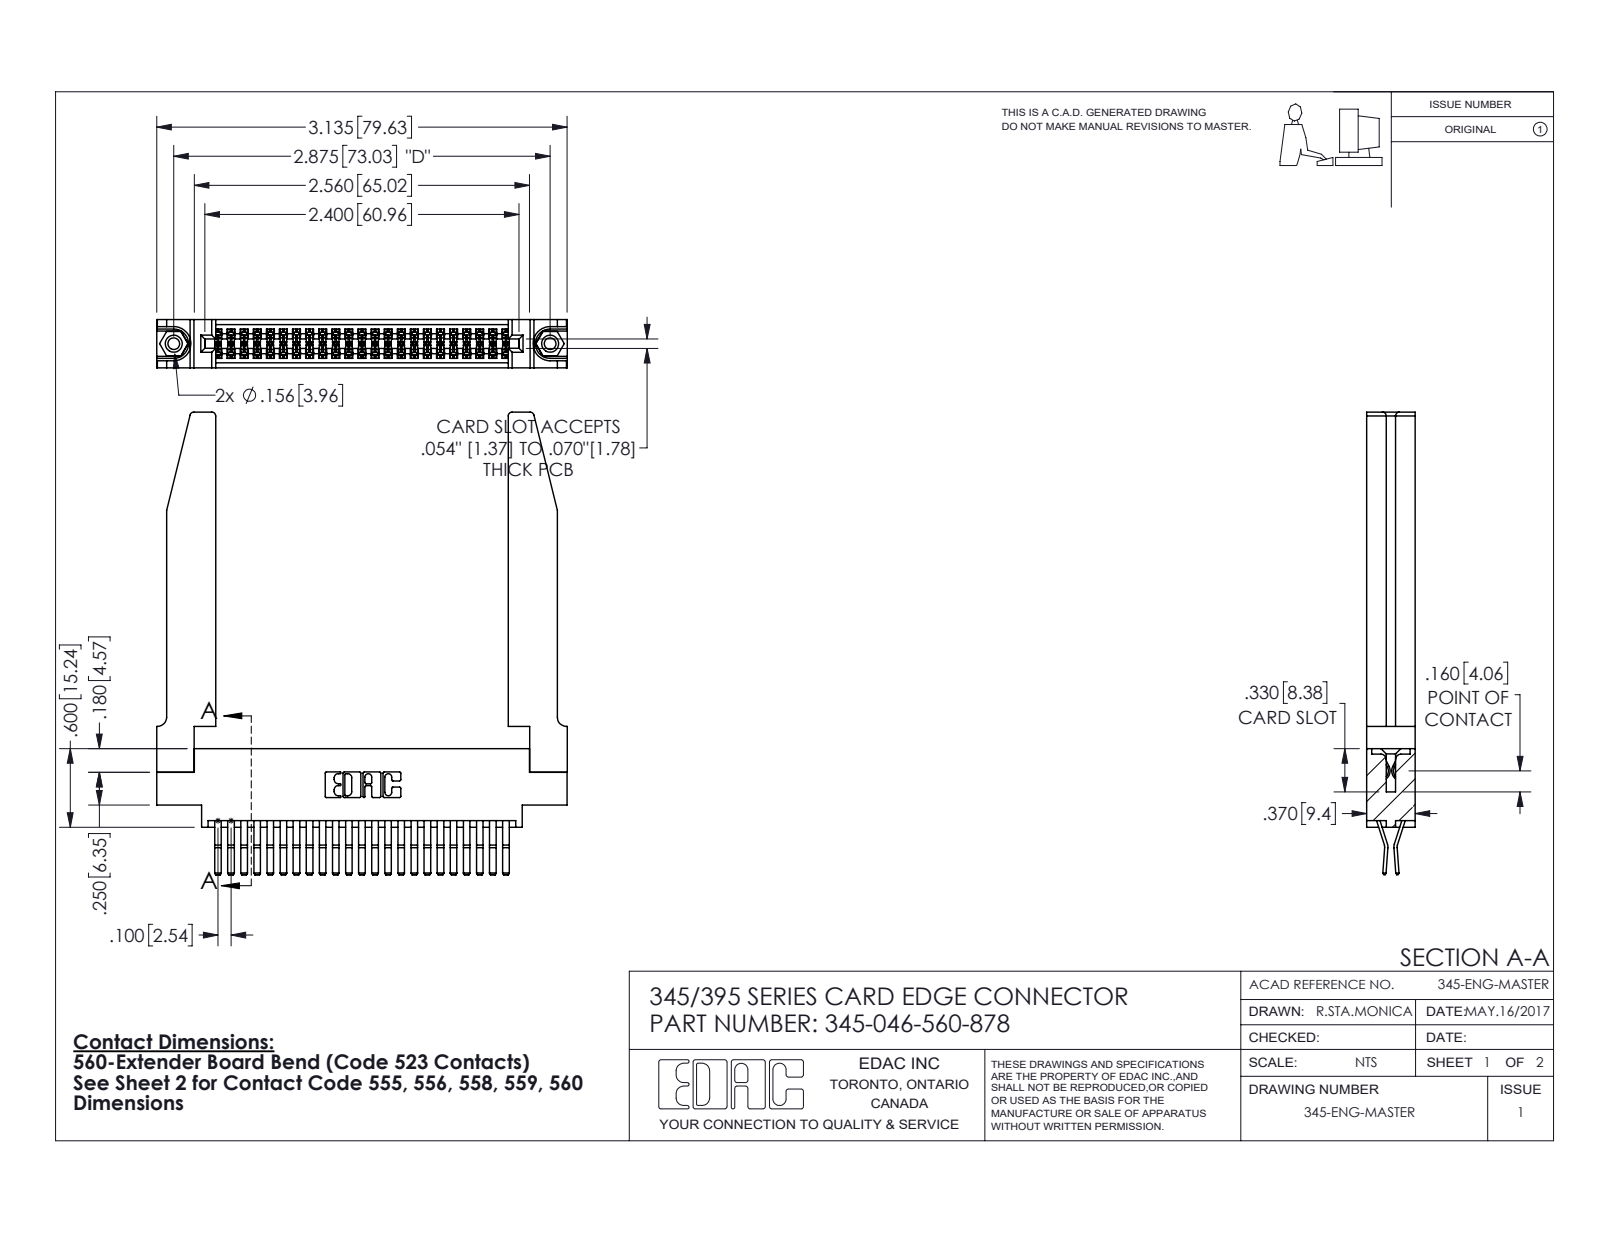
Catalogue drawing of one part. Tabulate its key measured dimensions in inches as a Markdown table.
| quantity | value |
| --- | --- |
| part name | 345-220-078_345-220-078; 345 Part_0.170 Offset - 0.156 Dia-TH; 345-250-001_345-250-001-102; 345-046-560-878 (+1 more) |
| STEP written by | SolidWorks 2016 (CONFIG_CONTROL_DESIGN) |
| units | inches |
| bodies | 51 solids, 2756 faces (1744 planar, 960 cylindrical, 52 other) |
| overall size | 3.532 × 3.136 × 0.37 |
| volume | 0.947 in³ |
| surface area | 29.21 in² |
| round holes (diameter × count) | 0.089 × 2, 0.125 × 2, 0.156 × 2, 0.064 × 1 |
| round bosses / shafts (diameter × count) | 0.155 × 2 |
| partial cylindrical surfaces (radius × count) | 0.006 × 69, 0.01 × 22, 0.03 × 8, 0.007 × 6, 0.031 × 6, 0.026 × 3, 0.01 × 2, 0.014 × 2 |
| main face-to-face distances | 0.37, 0.072, 0.298, 0.025, 0.098, 0.272, 0.2, 0.225, 0.148, 0.15 |
| hole center spacings | 0.27, 2.641, 2.875 |
